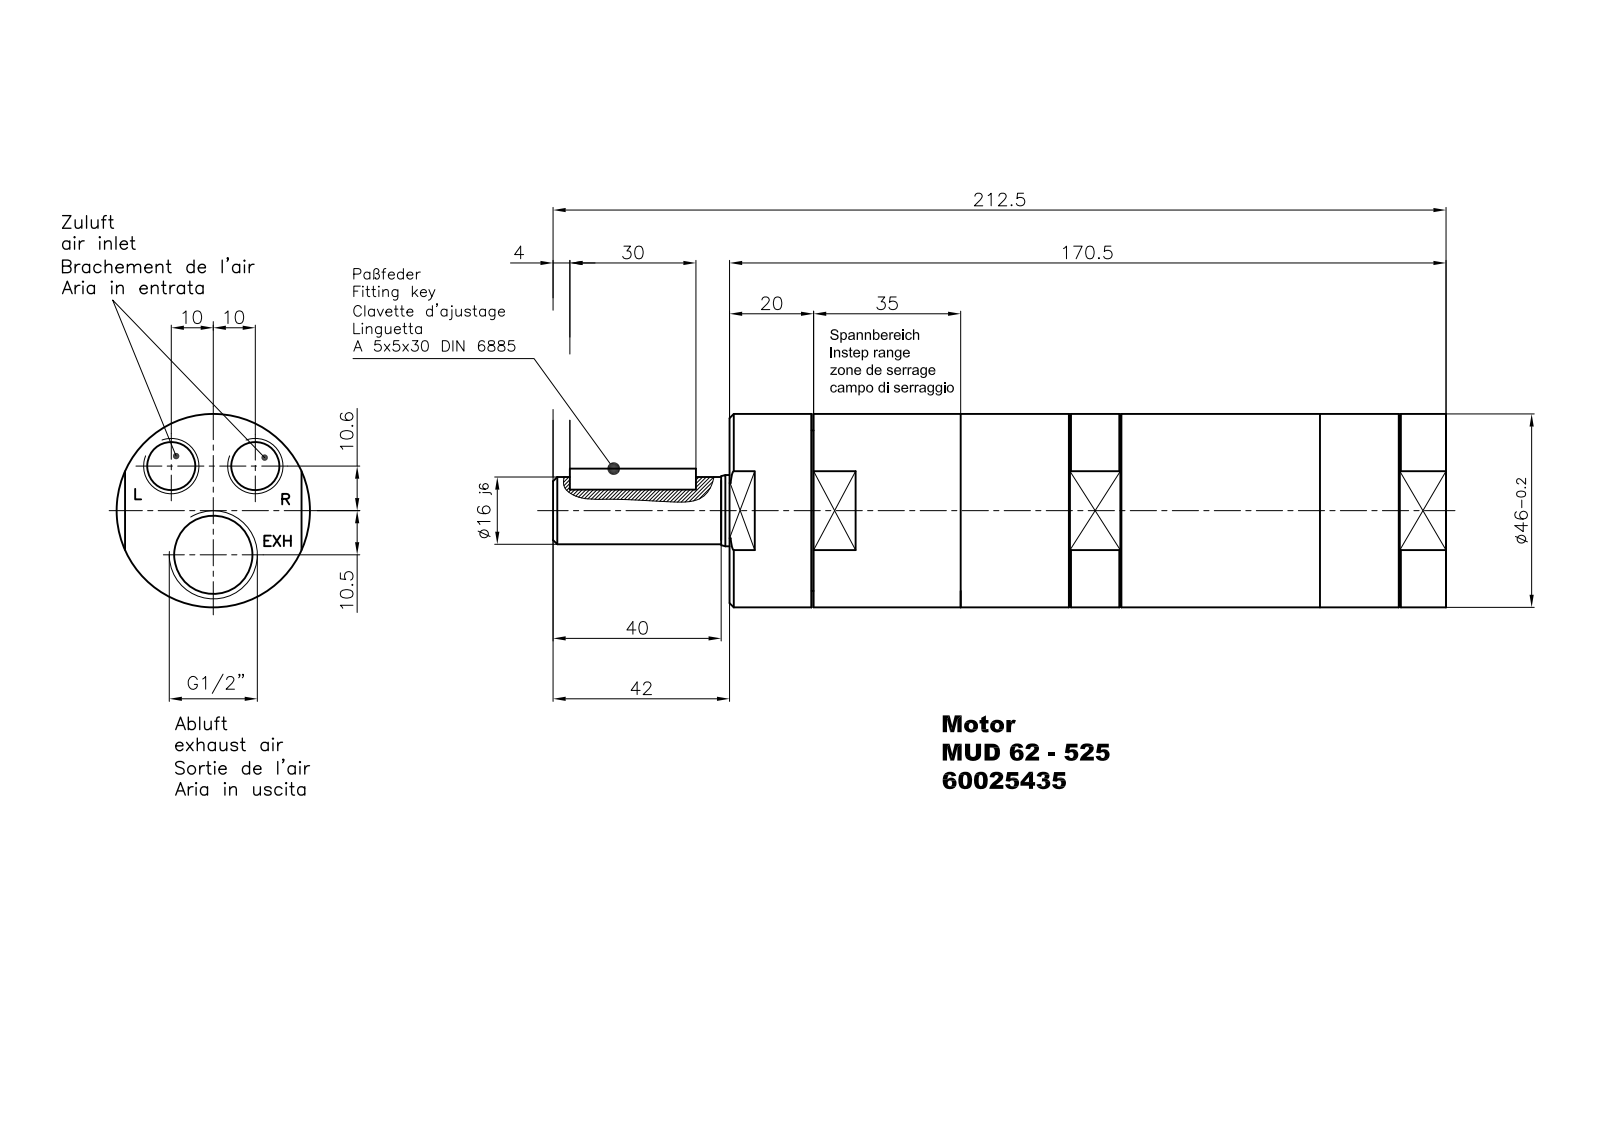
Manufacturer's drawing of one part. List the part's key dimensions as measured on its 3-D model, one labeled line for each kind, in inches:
Part name (STEP PRODUCT): MUD 62-212
STEP written by: Autodesk Inventor 2012 (AUTOMOTIVE_DESIGN)
Units: inches
Bodies: 1 solid, 138 faces (94 planar, 19 cylindrical, 25 other)
Overall size (bounding box): 8.366 × 1.811 × 1.811
Volume: 17.29 in³ · Surface area: 53.08 in²
Round holes (diameter × count): ⌀0.451 ×2, ⌀0.063 ×1, ⌀0.689 ×1, ⌀0.733 ×1
Round bosses / shafts (diameter × count): ⌀1.811 ×1, ⌀1.502 ×1, ⌀0.667 ×1, ⌀0.63 ×1
Partial cylindrical surfaces — rounded edges, fillets, slot ends (radius × count): R0.098 ×2
Main face-to-face distances: 6.713, 1.654, 1.181, 5.531, 2.165, 4.547, 3.366, 0.768, 5.925, 1.398
Hole centre spacings: 0.574, 0.919, 0.413, 0.787
